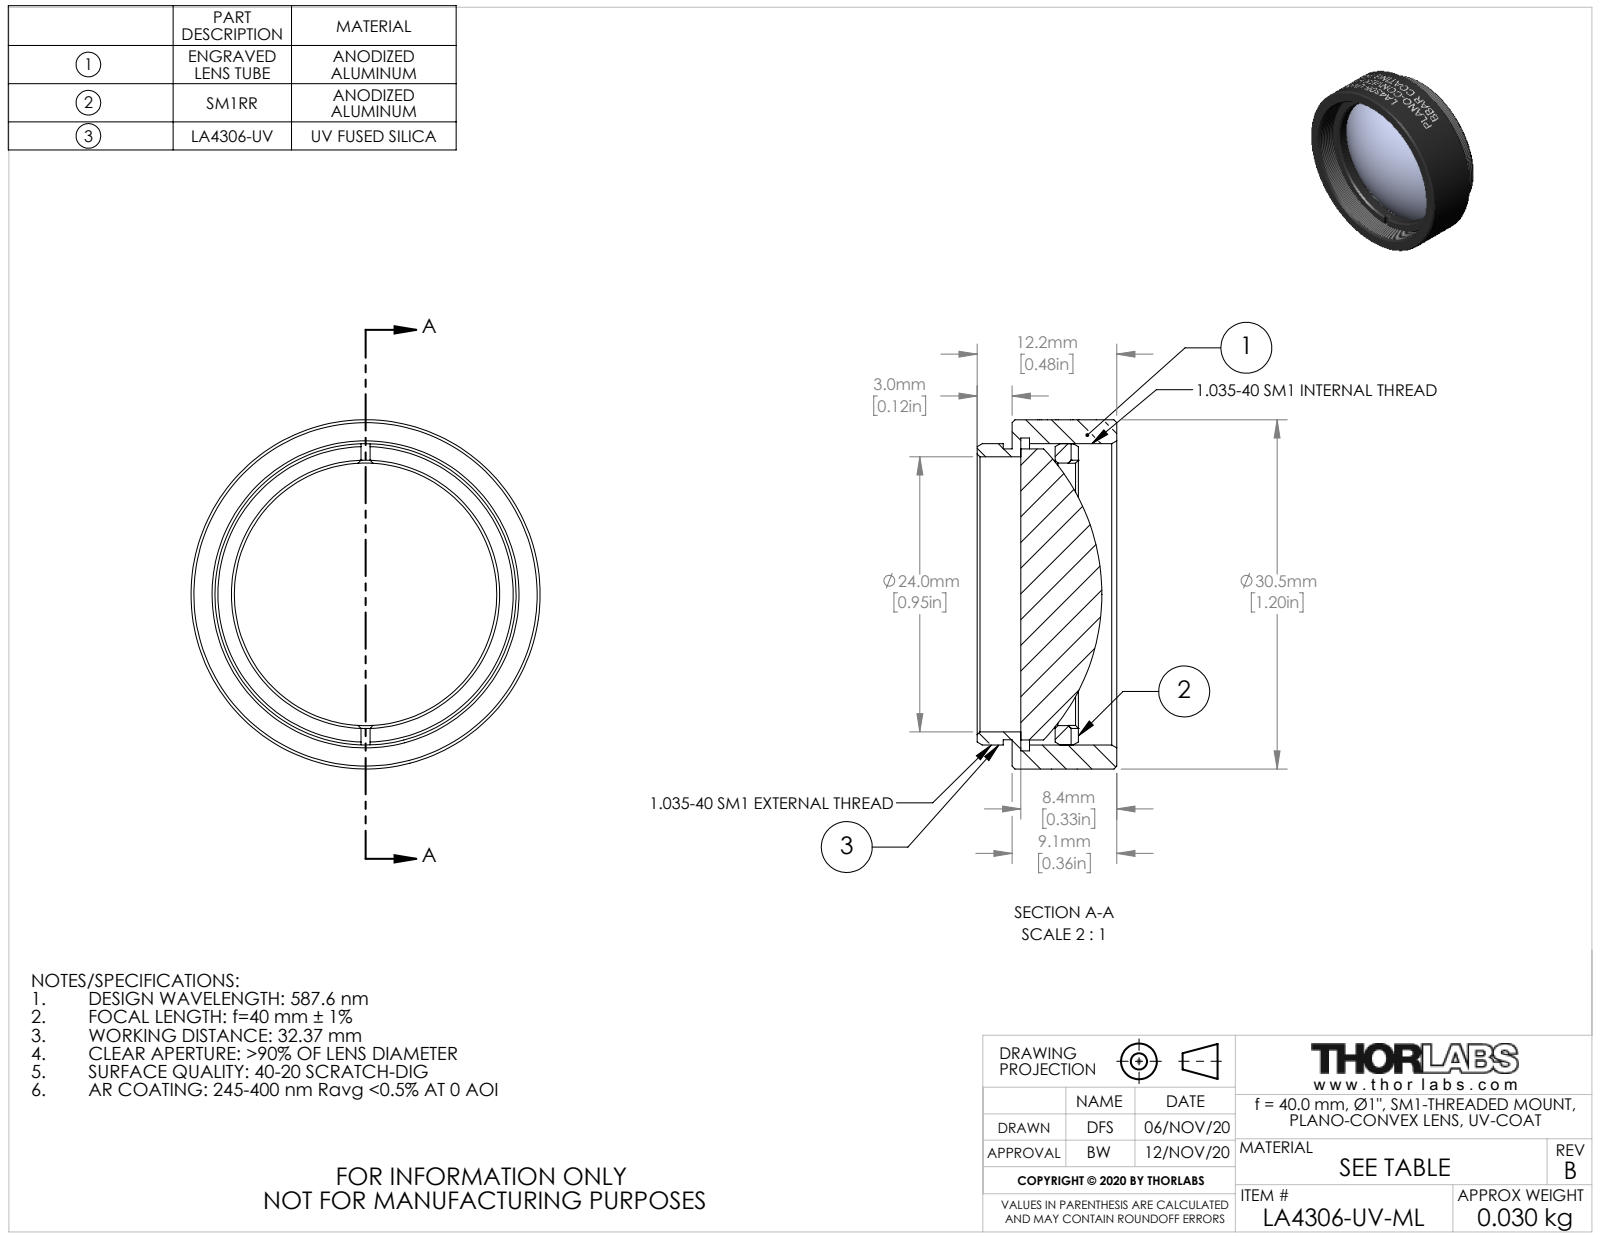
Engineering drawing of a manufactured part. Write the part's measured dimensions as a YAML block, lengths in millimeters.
part_name: "24459-E0W"
step_written_by: "SolidWorks 2018 (CONFIG_CONTROL_DESIGN)"
units: millimeters
bodies: {solids: 3, faces: 157, planar: 20, cylindrical: 113, other: 24}
overall_size: [30.48, 30.48, 12.19]
volume: 4592
surface_area: 4529
round_holes:
  - {diameter: 22.91, count: 1}
  - {diameter: 24, count: 1}
  - {diameter: 27.3, count: 1}
round_bosses_or_shafts:
  - {diameter: 30.48, count: 1}
  - {diameter: 26.29, count: 1}
  - {diameter: 25.4, count: 1}
  - {diameter: 25.37, count: 1}
face_to_face_distances: [0.76, 9.14, 8.38, 3.76, 3, 5.38, 5.79, 5.03, 2.03, 3.35]
